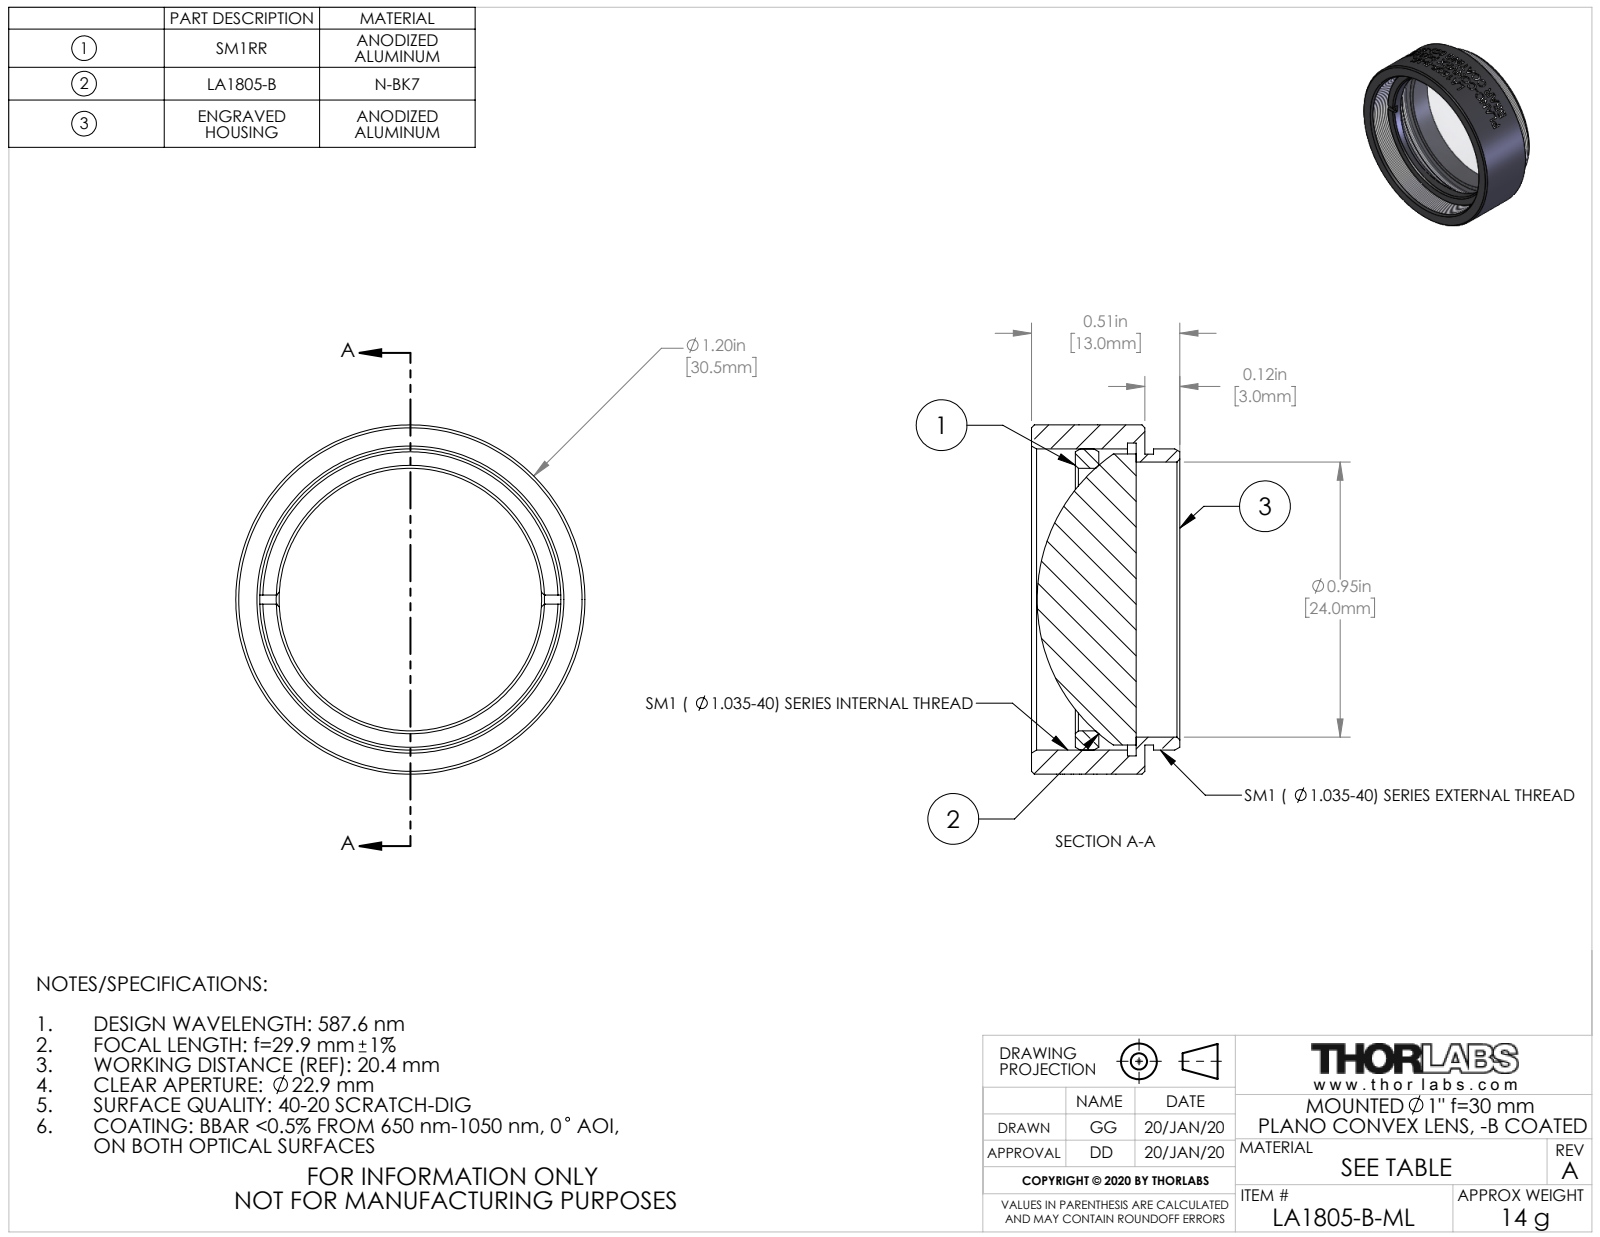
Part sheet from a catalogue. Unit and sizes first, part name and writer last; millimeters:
Units: millimetres
Overall size (bounding box): 30.48 × 30.48 × 12.95
Round holes (diameter × count): ⌀22.91 ×1, ⌀24 ×1, ⌀26.29 ×1, ⌀27.3 ×1
Round bosses / shafts (diameter × count): ⌀30.48 ×1, ⌀26.29 ×1, ⌀25.4 ×1, ⌀25.37 ×1
Main face-to-face distances: 0.76, 9.91, 9.15, 4.03, 3.27, 5.88, 6.06, 5.3, 2.03, 3.85
Volume: 5 212 mm³ · Surface area: 4 722 mm²
Bodies: 3 solids, 158 faces (20 planar, 114 cylindrical, 24 other)
Part name (STEP PRODUCT): TTN203734-E0W
STEP written by: SolidWorks 2018 (CONFIG_CONTROL_DESIGN)
